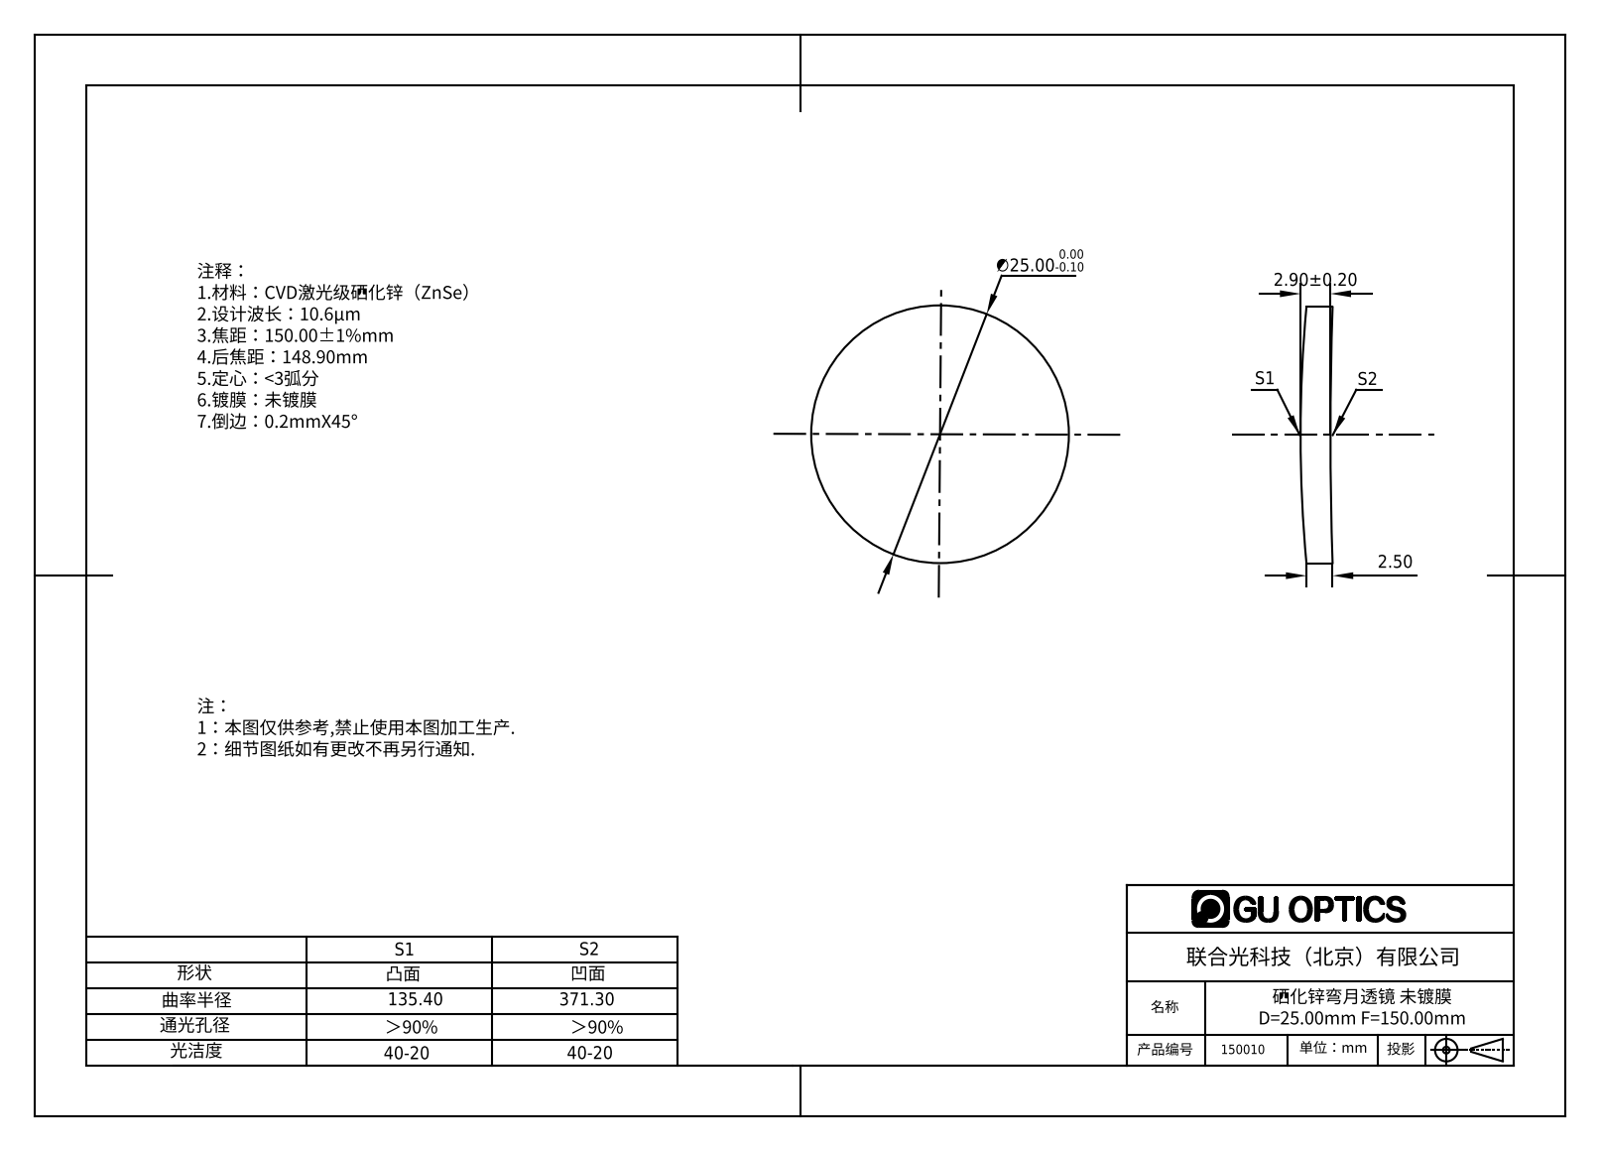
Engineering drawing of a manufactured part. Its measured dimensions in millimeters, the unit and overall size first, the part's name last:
Units: millimetres
Overall size (bounding box): 25 × 25 × 3.11
Round bosses / shafts (diameter × count): ⌀25 ×1
Volume: 1 333 mm³ · Surface area: 1 182 mm²
Bodies: 1 solid, 6 faces (0 planar, 2 cylindrical, 4 other)
Part name (STEP PRODUCT): 150010
STEP written by: SolidWorks 2016 (AUTOMOTIVE_DESIGN)
